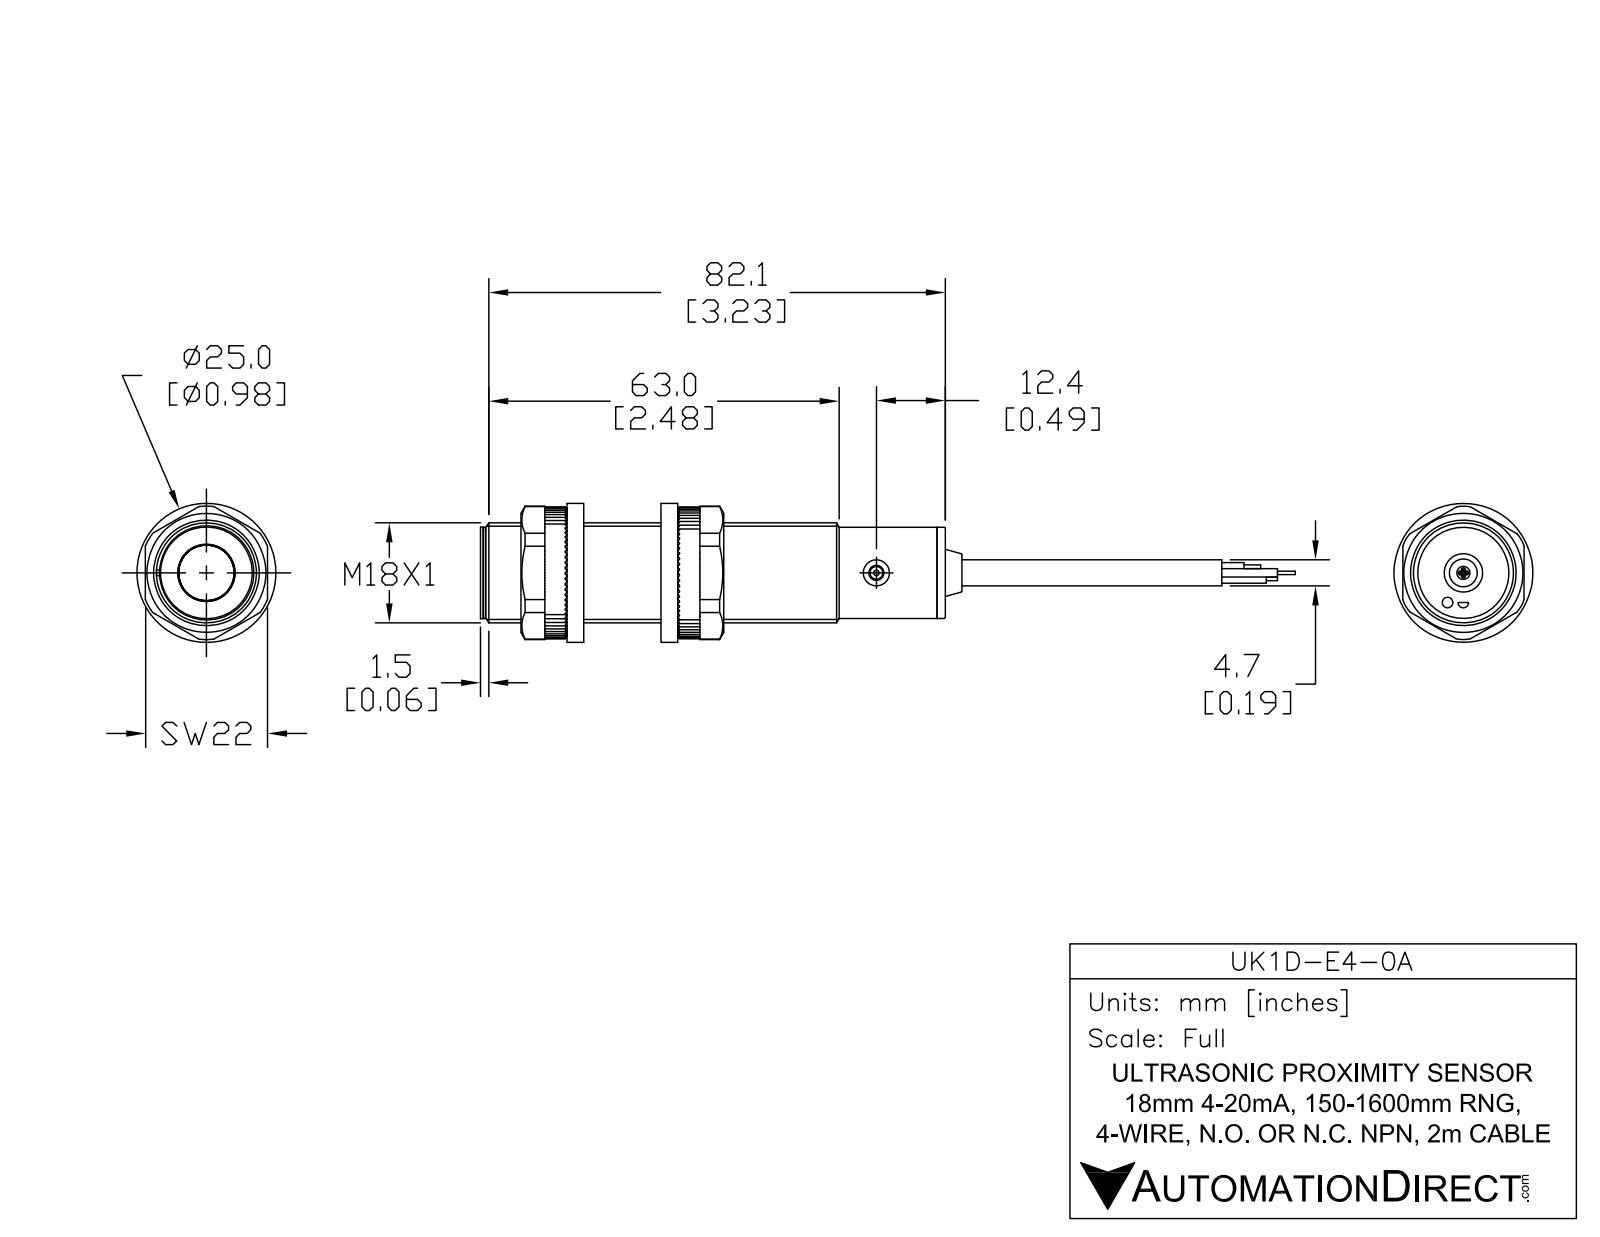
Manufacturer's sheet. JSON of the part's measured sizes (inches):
{"part_name": "UK1D-E4-0A", "step_written_by": "SolidWorks 2017 (AUTOMOTIVE_DESIGN)", "units": "inches", "bodies": {"solids": 6, "faces": 55, "planar": 17, "cylindrical": 24, "other": 14}, "overall_size": [4.832, 0.709, 0.709], "volume_in3": 1.285, "surface_area_in2": 10.69, "round_holes": [[0.185, 2], [0.106, 1]], "round_bosses_or_shafts": [[0.709, 1], [0.646, 1], [0.622, 1], [0.374, 1], [0.189, 1], [0.091, 1]], "face_to_face_distances": [3.193, 3.252, 0.059, 0.039, 3.232, 3.291, 0.041, 3.234, 3.293, 3.257]}
